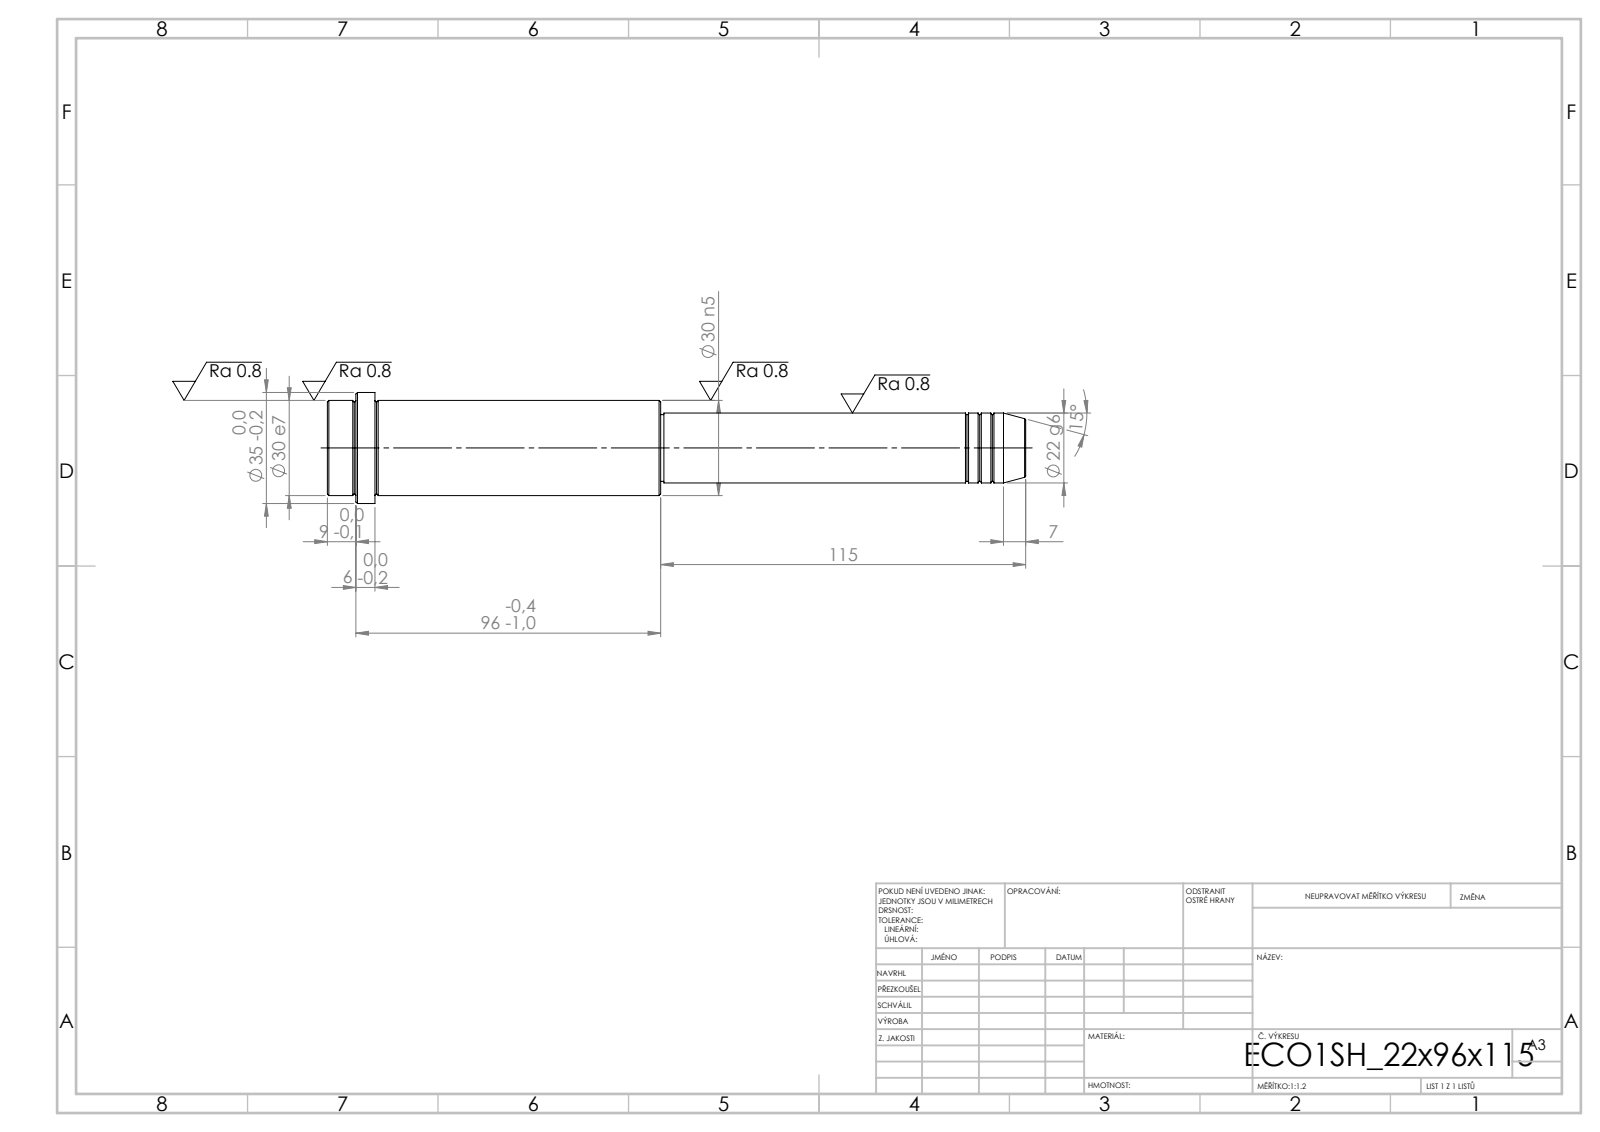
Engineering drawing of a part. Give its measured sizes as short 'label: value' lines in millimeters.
written by: SolidWorks 2019 (CONFIG_CONTROL_DESIGN)
unit: mm
bodies: 1 solid, 52 faces (6 planar, 16 cylindrical, 30 other)
size: 220 × 35 × 35
volume: 118 814 mm³; area: 19 898 mm²
bosses: 1× ⌀35, 1× ⌀30, 1× ⌀22, 1× ⌀21
face distances: 105, 90, 15, 115, 205, 220, 211, 96, 6, 9
